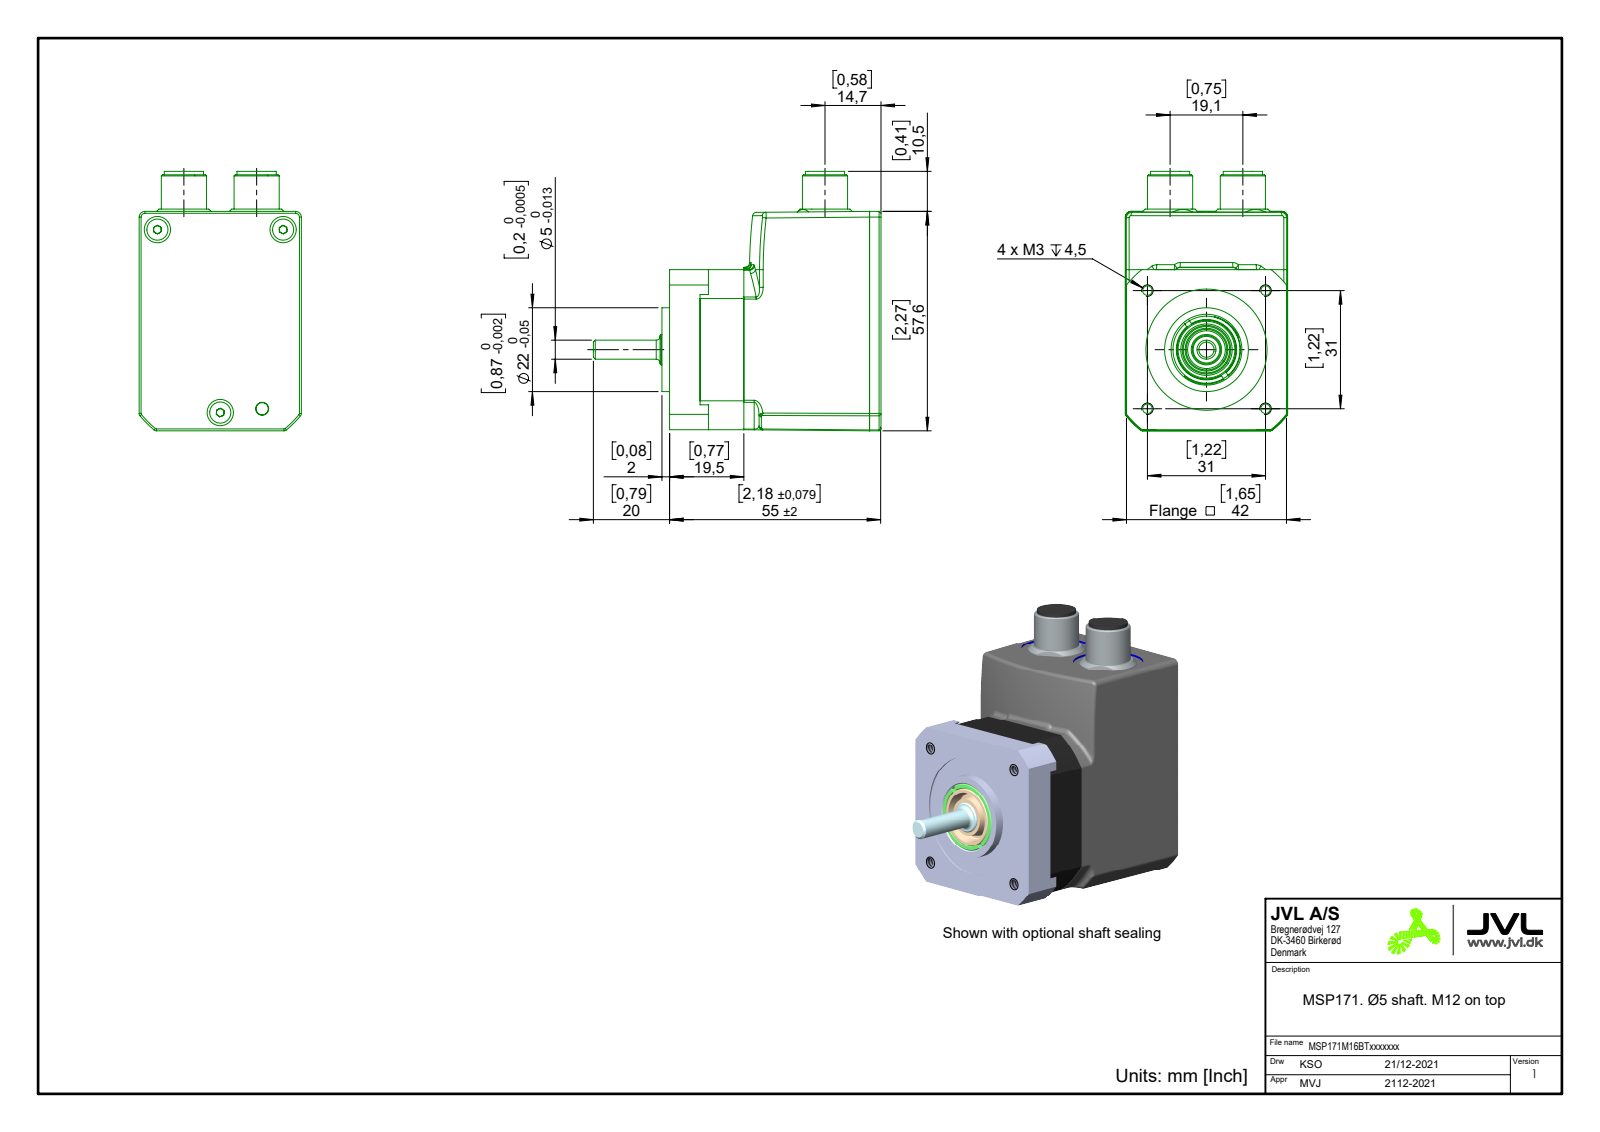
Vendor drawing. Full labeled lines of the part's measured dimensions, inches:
Part name (STEP PRODUCT): MSP171M16BTxxxxxxx
STEP written by: FreeCAD (AUTOMOTIVE_DESIGN)
Units: inches
Bodies: 5 solids, 332 faces (135 planar, 73 cylindrical, 124 other)
Overall size (bounding box): 2.972 × 2.68 × 1.676
Volume: 7.317 in³ · Surface area: 28.7 in²
Round holes (diameter × count): ⌀0.098 ×4, ⌀0.13 ×3, ⌀0.724 ×2, ⌀0.11 ×1, ⌀0.134 ×1, ⌀0.354 ×1, ⌀0.394 ×1, ⌀1.252 ×1
Round bosses / shafts (diameter × count): ⌀0.218 ×3, ⌀0.118 ×3, ⌀0.594 ×2, ⌀0.467 ×2, ⌀0.406 ×2, ⌀0.866 ×1, ⌀0.61 ×1, ⌀0.547 ×1
Partial cylindrical surfaces — rounded edges, fillets, slot ends (radius × count): R0.039 ×13, R0.059 ×2, R0.346 ×1, R0.981 ×1, R1.004 ×1, R1.063 ×1, R1.074 ×1, R3.15 ×1
Main face-to-face distances: 1.654, 2.185, 0.079, 2.165, 0.02, 1.665, 0.059, 2.106, 0.098, 0.157
Hole centre spacings: 0.863, 1.22, 1.4, 0.611, 0.631, 1.409, 1.726, 1.851
